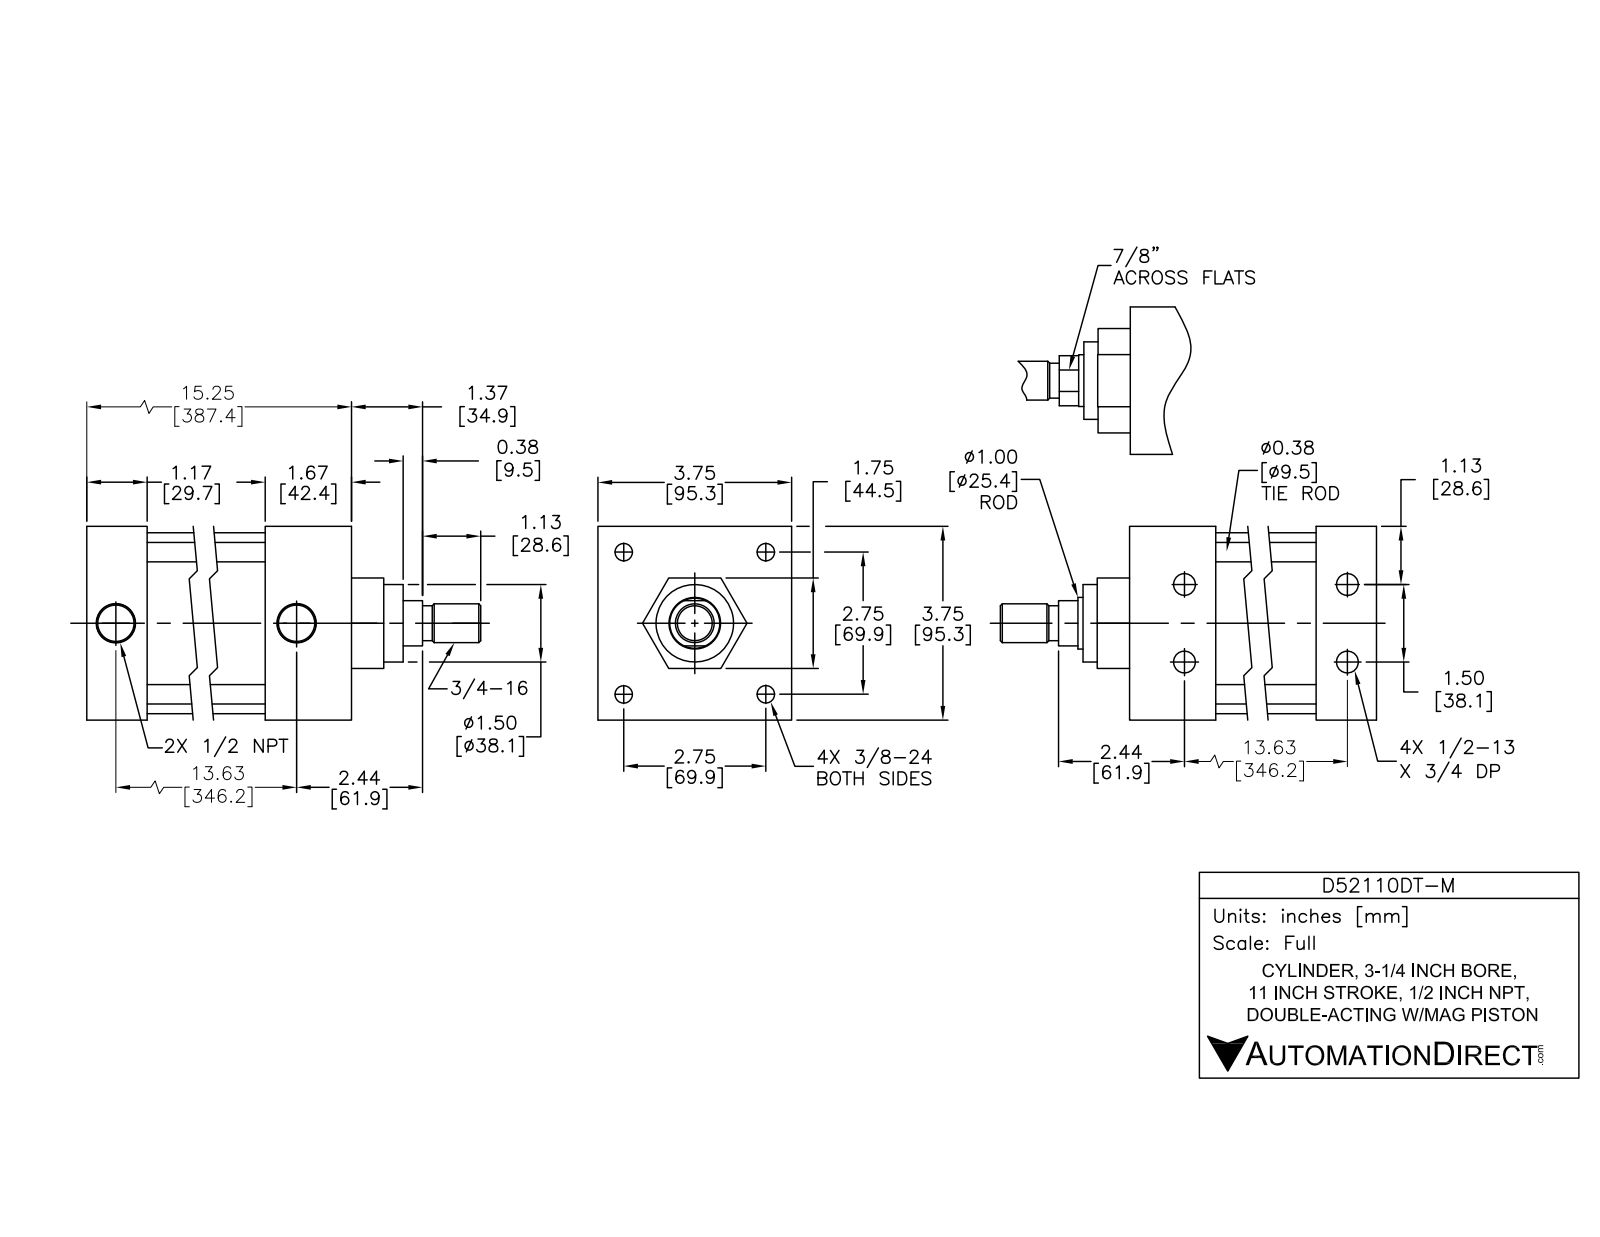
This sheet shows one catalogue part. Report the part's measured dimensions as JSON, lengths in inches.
{"part_name": "D52110DT-M BODY; D52110DT-M PISTON; D52110DT-M", "step_written_by": "SolidWorks 2015 (AUTOMOTIVE_DESIGN)", "units": "inches", "bodies": {"solids": 12, "faces": 303, "planar": 99, "cylindrical": 114, "other": 90}, "overall_size": [17.745, 3.75, 3.75], "volume_in3": 80.99, "surface_area_in2": 551.8, "round_holes": [[0.33, 4], [0.406, 4], [0.417, 4], [0.625, 4], [0.5, 2], [0.766, 2], [1, 1], [1.003, 1], [3.25, 1]], "round_bosses_or_shafts": [[0.609, 4], [0.375, 4], [0.34, 4], [3.5, 1], [3.247, 1], [1.75, 1], [0.997, 1], [0.97, 1]], "partial_cylinders_radius": [[0.375, 4]], "face_to_face_distances": [3.75, 0.08, 12.326, 15.246, 1.75, 13.997, 1.249, 12.751, 1.246, 2.495], "hole_center_spacings": [2.758, 1.95, 0.75, 0.76, 1.5, 3.9, 13.5, 13.525]}
